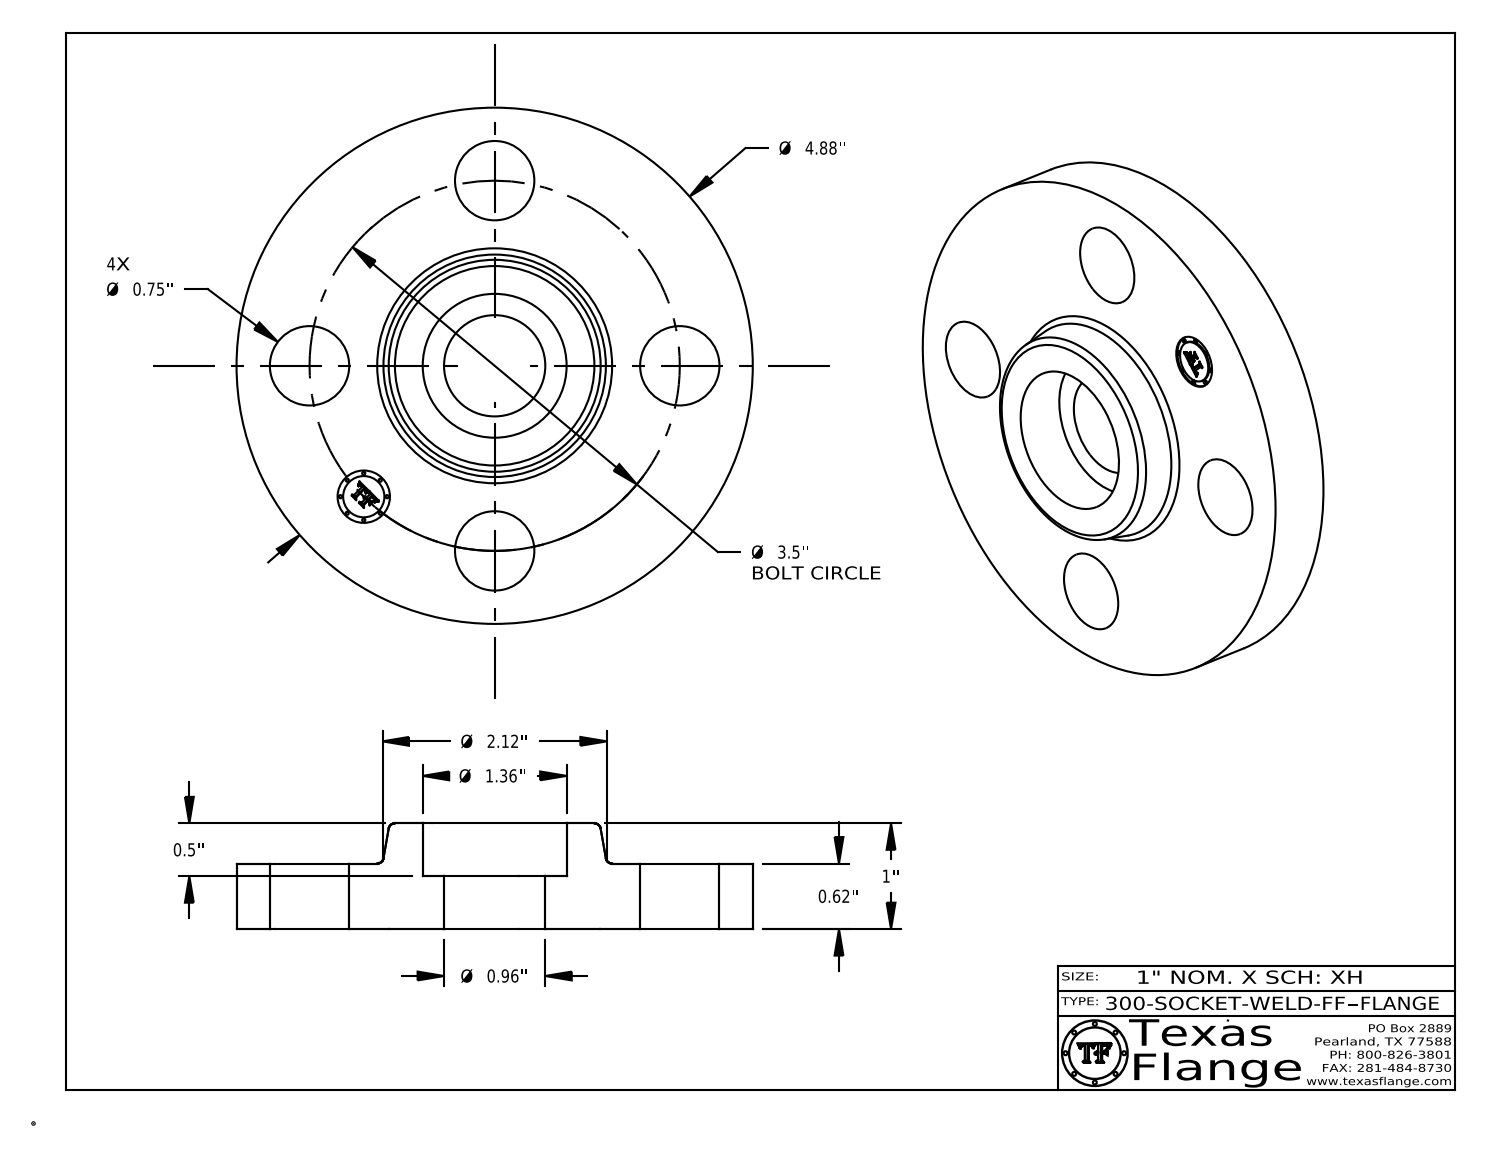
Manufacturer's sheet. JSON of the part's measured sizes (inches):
{"part_name": "300-SOCKET-WELD-FF", "step_written_by": "CATIA V5 STEP AP214 (AUTOMOTIVE_DESIGN)", "units": "inches", "bodies": {"solids": 1, "faces": 410, "planar": 370, "cylindrical": 34, "other": 6}, "overall_size": [4.88, 4.88, 1], "volume_in3": 10.67, "surface_area_in2": 53.35, "round_holes": [[0.75, 4], [0.495, 1], [0.957, 1], [1.36, 1]], "round_bosses_or_shafts": [[0.03, 8], [4.88, 1], [0.39, 1]], "face_to_face_distances": [0.62, 0.5, 1, 0.38, 0.12, 0.105, 0.015, 0.605, 0.395, 0.148], "hole_center_spacings": [1.75, 2.475, 1.339, 3.233, 3.5]}
